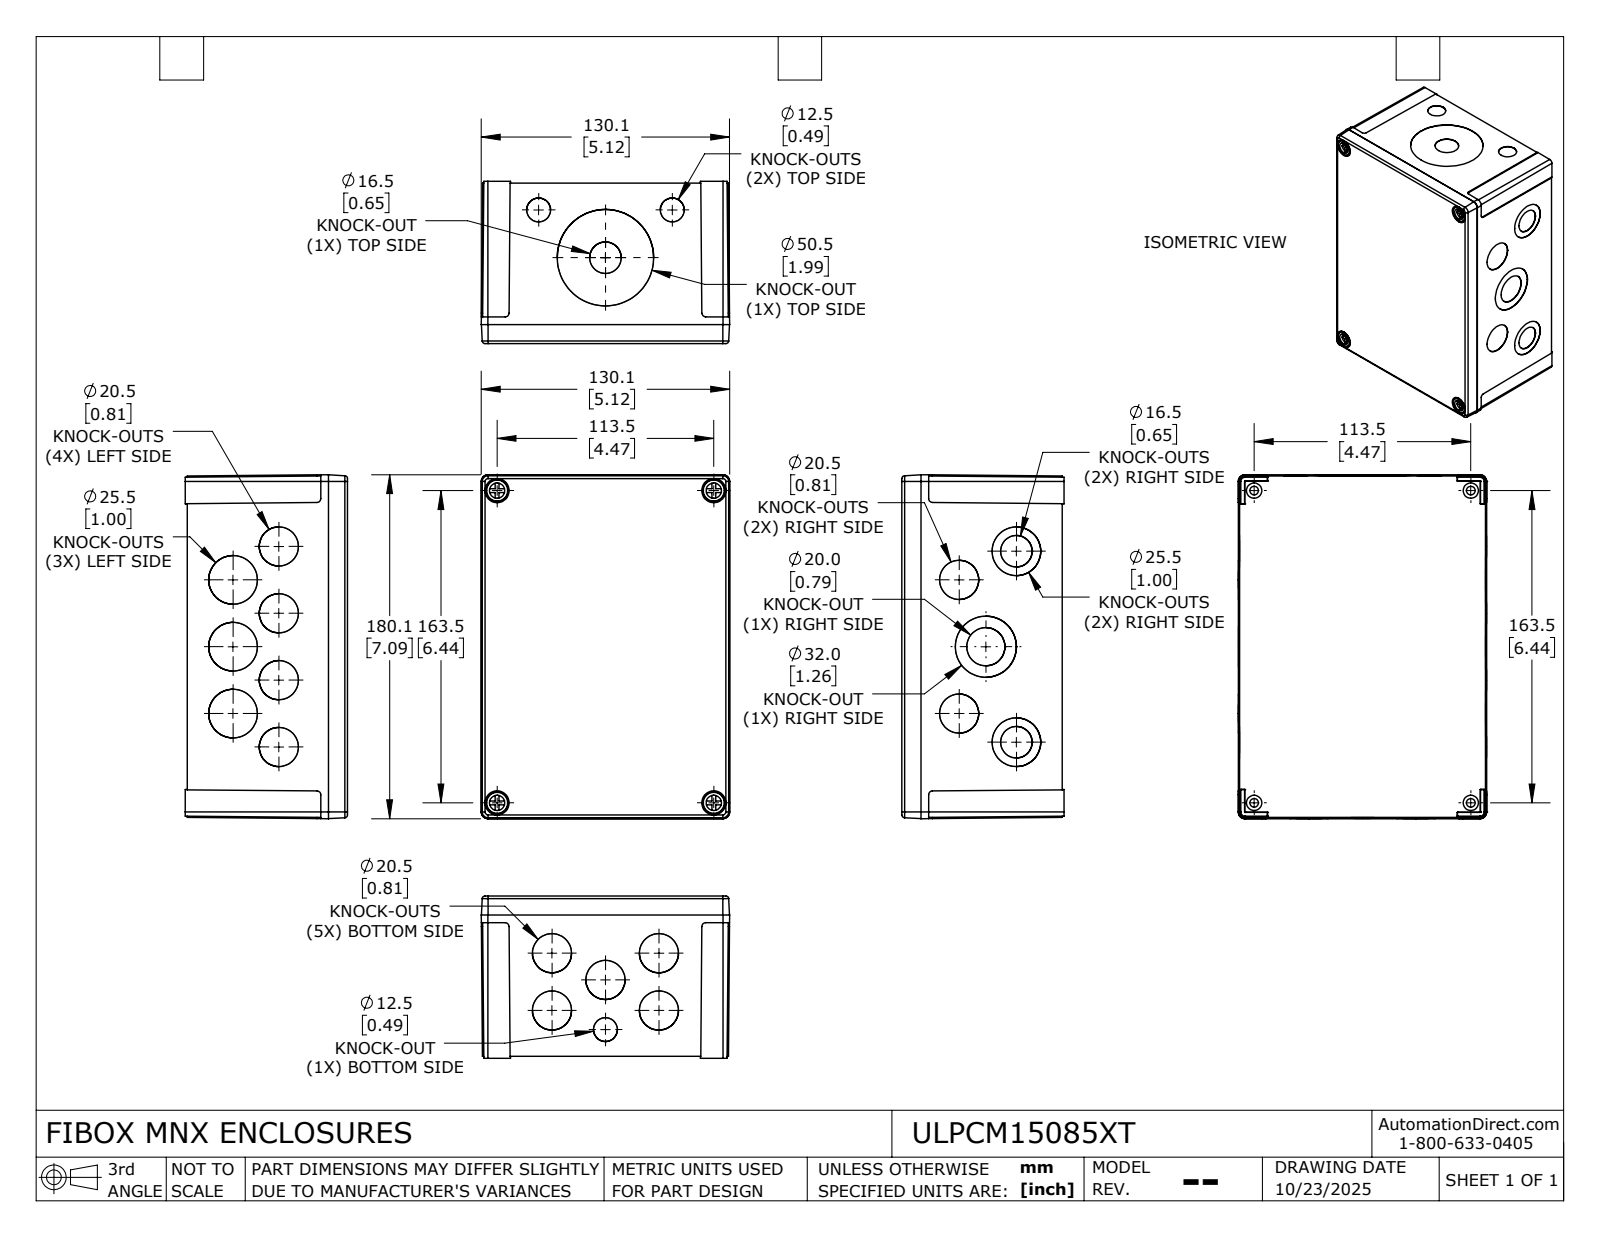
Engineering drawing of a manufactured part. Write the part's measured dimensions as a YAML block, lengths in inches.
part_name: "ULPCM15085XT_Default"
step_written_by: "SolidWorks 2024 (CONFIG_CONTROL_DESIGN)"
units: inches
bodies: {solids: 6, faces: 564, planar: 290, cylindrical: 222, other: 52}
overall_size: [7.091, 5.122, 3.346]
volume: 22.34
surface_area: 316.7
round_holes:
  - {diameter: 0.807, count: 11}
  - {diameter: 0.126, count: 8}
  - {diameter: 0.157, count: 8}
  - {diameter: 1.004, count: 5}
  - {diameter: 0.177, count: 4}
  - {diameter: 0.315, count: 4}
  - {diameter: 0.457, count: 4}
  - {diameter: 0.492, count: 3}
  - {diameter: 0.65, count: 3}
  - {diameter: 0.787, count: 1}
  - {diameter: 1.26, count: 1}
  - {diameter: 1.988, count: 1}
round_bosses_or_shafts:
  - {diameter: 0.315, count: 8}
  - {diameter: 0.098, count: 8}
  - {diameter: 0.433, count: 4}
  - {diameter: 0.283, count: 4}
partial_cylinders:
  - {radius: 0.039, count: 16}
  - {radius: 0.056, count: 6}
  - {radius: 0.021, count: 4}
  - {radius: 0.059, count: 4}
  - {radius: 0.079, count: 4}
  - {radius: 0.197, count: 4}
  - {radius: 0.023, count: 2}
face_to_face_distances: [0.165, 3.307, 0.126, 3.181, 0.118, 3.189, 3.063, 0.158, 0.026, 0.019]
hole_center_spacings: [1.169, 1.378, 2.756, 1.333, 1.939, 1.969, 2.273, 2.281]
